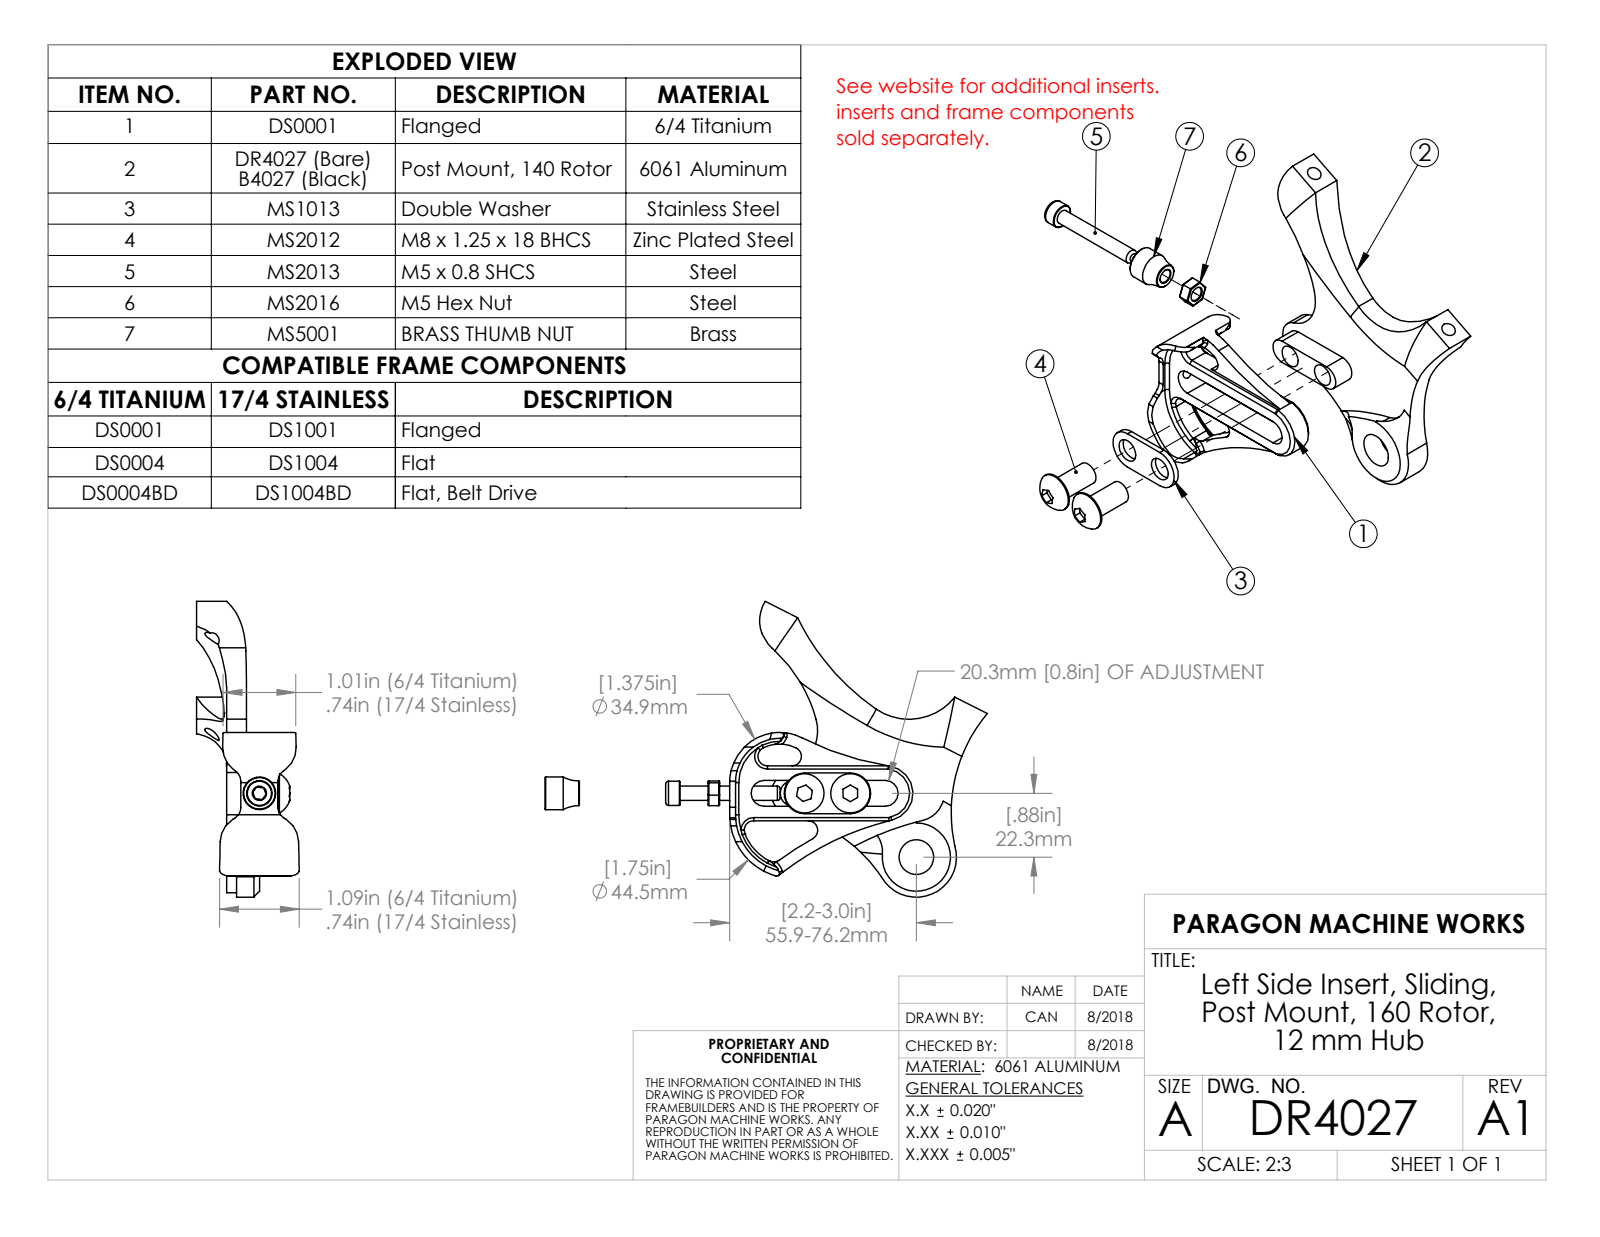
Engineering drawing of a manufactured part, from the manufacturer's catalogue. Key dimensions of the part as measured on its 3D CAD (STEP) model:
Part name (STEP PRODUCT): DR4027
STEP written by: SolidWorks 2023 (AUTOMOTIVE_DESIGN)
Units: inches
Bodies: 1 solid, 53 faces (14 planar, 30 cylindrical, 9 other)
Overall size (bounding box): 4.066 × 3.129 × 1
Volume: 1.713 in³ · Surface area: 18.42 in²
Round holes (diameter × count): ⌀0.198 ×2, ⌀0.312 ×2, ⌀0.477 ×1
Partial cylindrical surfaces — rounded edges, fillets, slot ends (radius × count): R0.178 ×2, R0.6 ×2, R0.3 ×1, R0.385 ×1, R0.394 ×1, R0.5 ×1, R0.551 ×1, R0.787 ×1
Main face-to-face distances: 0.274, 0.453, 0.179, 0.138, 0.136, 0.315, 0.413, 0.551, 0.687, 0.866
Hole centre spacings: 0.63, 1.262, 1.77, 2.926
